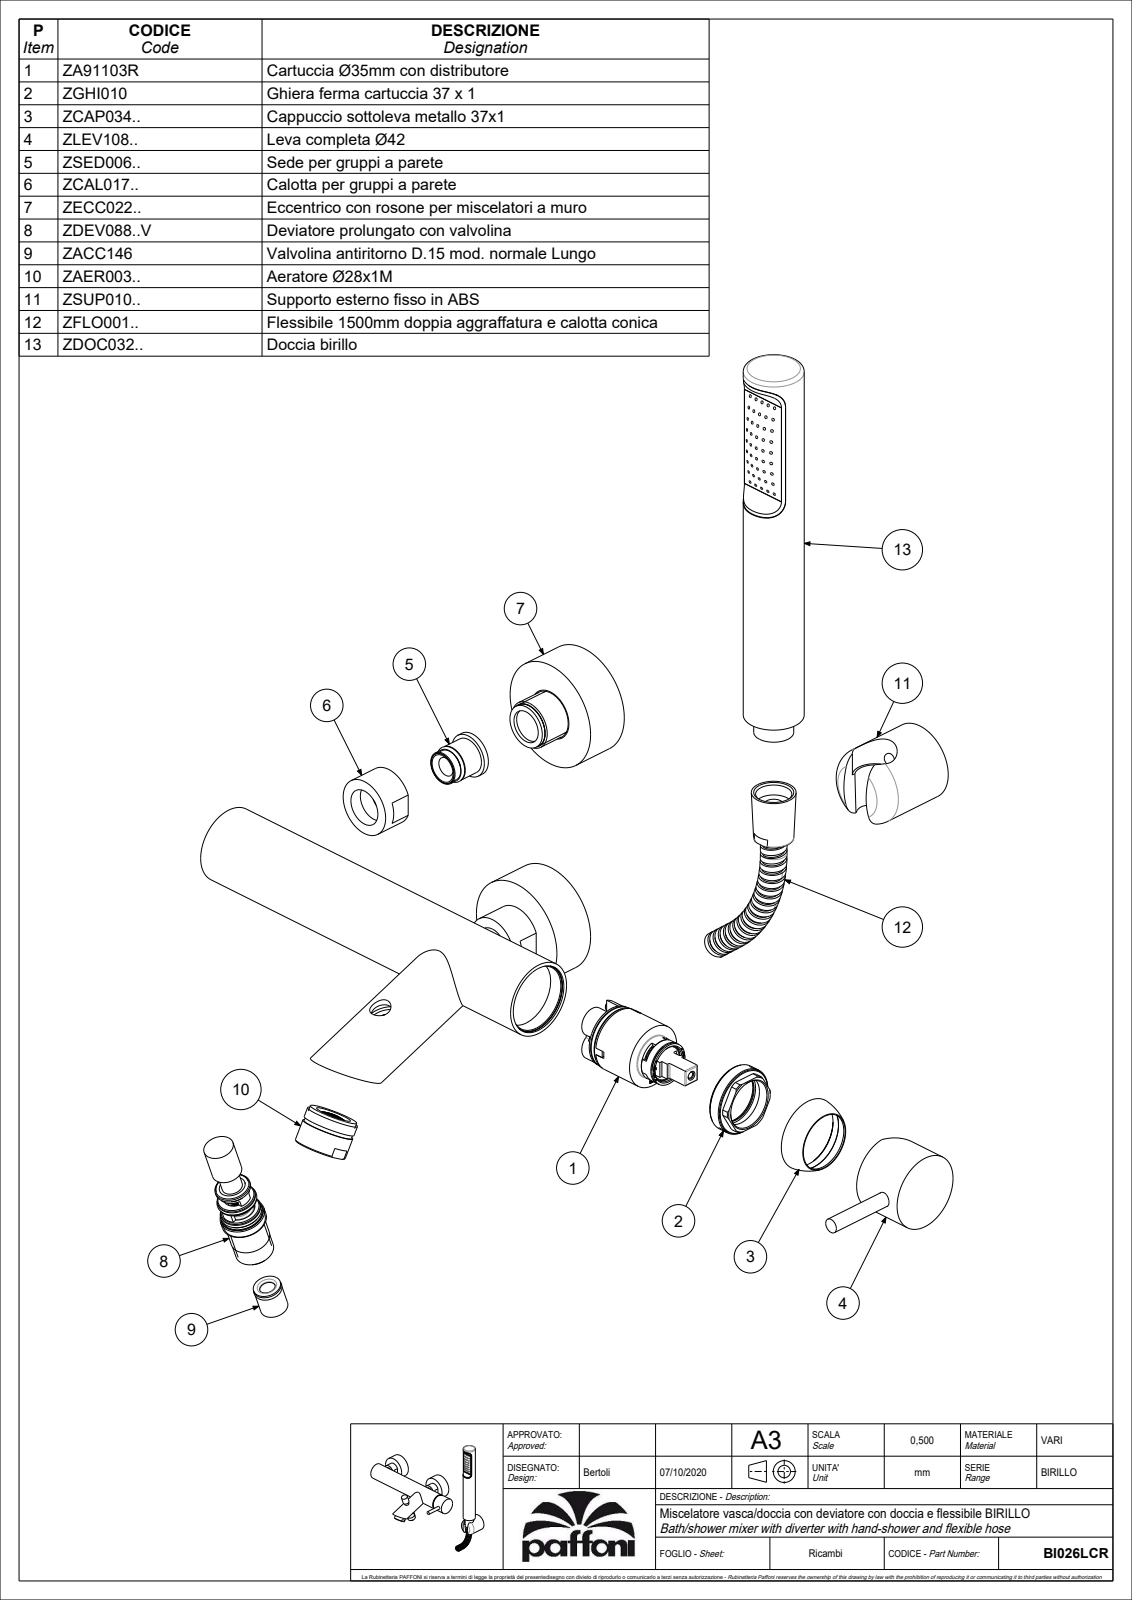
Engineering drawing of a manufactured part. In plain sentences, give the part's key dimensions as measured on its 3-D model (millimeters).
The part is named "BI026LCR". Its 3-D file was written by "CREO PARAMETRIC BY PTC INC, 2020044 (CONFIG_CONTROL_DESIGN)". It is 5 solids with 2877 faces: 2022 planar, 505 cylindrical and 350 other. Overall it measures 405.75 by 328.3 by 171.18 millimeters. Its volume is 496 535 cubic millimeters and its surface area 216 709 square millimeters. Round holes: 45 of diameter 1.5, 8 of diameter 5, 6 of diameter 7.5, 5 of diameter 8, 5 of diameter 12, 3 of diameter 9, 3 of diameter 16, 3 of diameter 18, 3 of diameter 24.5, 2 of diameter 4, 2 of diameter 10.5, 2 of diameter 16.7. Round bosses or shafts: 3 of diameter 24, 2 of diameter 59.5, 2 of diameter 35, 2 of diameter 31.5, 2 of diameter 21, 2 of diameter 20.8, 2 of diameter 19.7, 2 of diameter 12. Partial cylindrical surfaces (rounded edges, fillets, slot ends): 44 of radius 0.5, 11 of radius 0.15, 9 of radius 0.3, 4 of radius 1, 4 of radius 7, 2 of radius 4.5, 2 of radius 7.8, 2 of radius 7.95. The main face-to-face distances are 4.7, 19.5, 2, 3, 20, 39.5, 14.8, 1, 24.7, 10. The hole center spacings are 7.91, 13.76, 6.5, 13, 20.01, 26.39, 4.5, 19.5.
